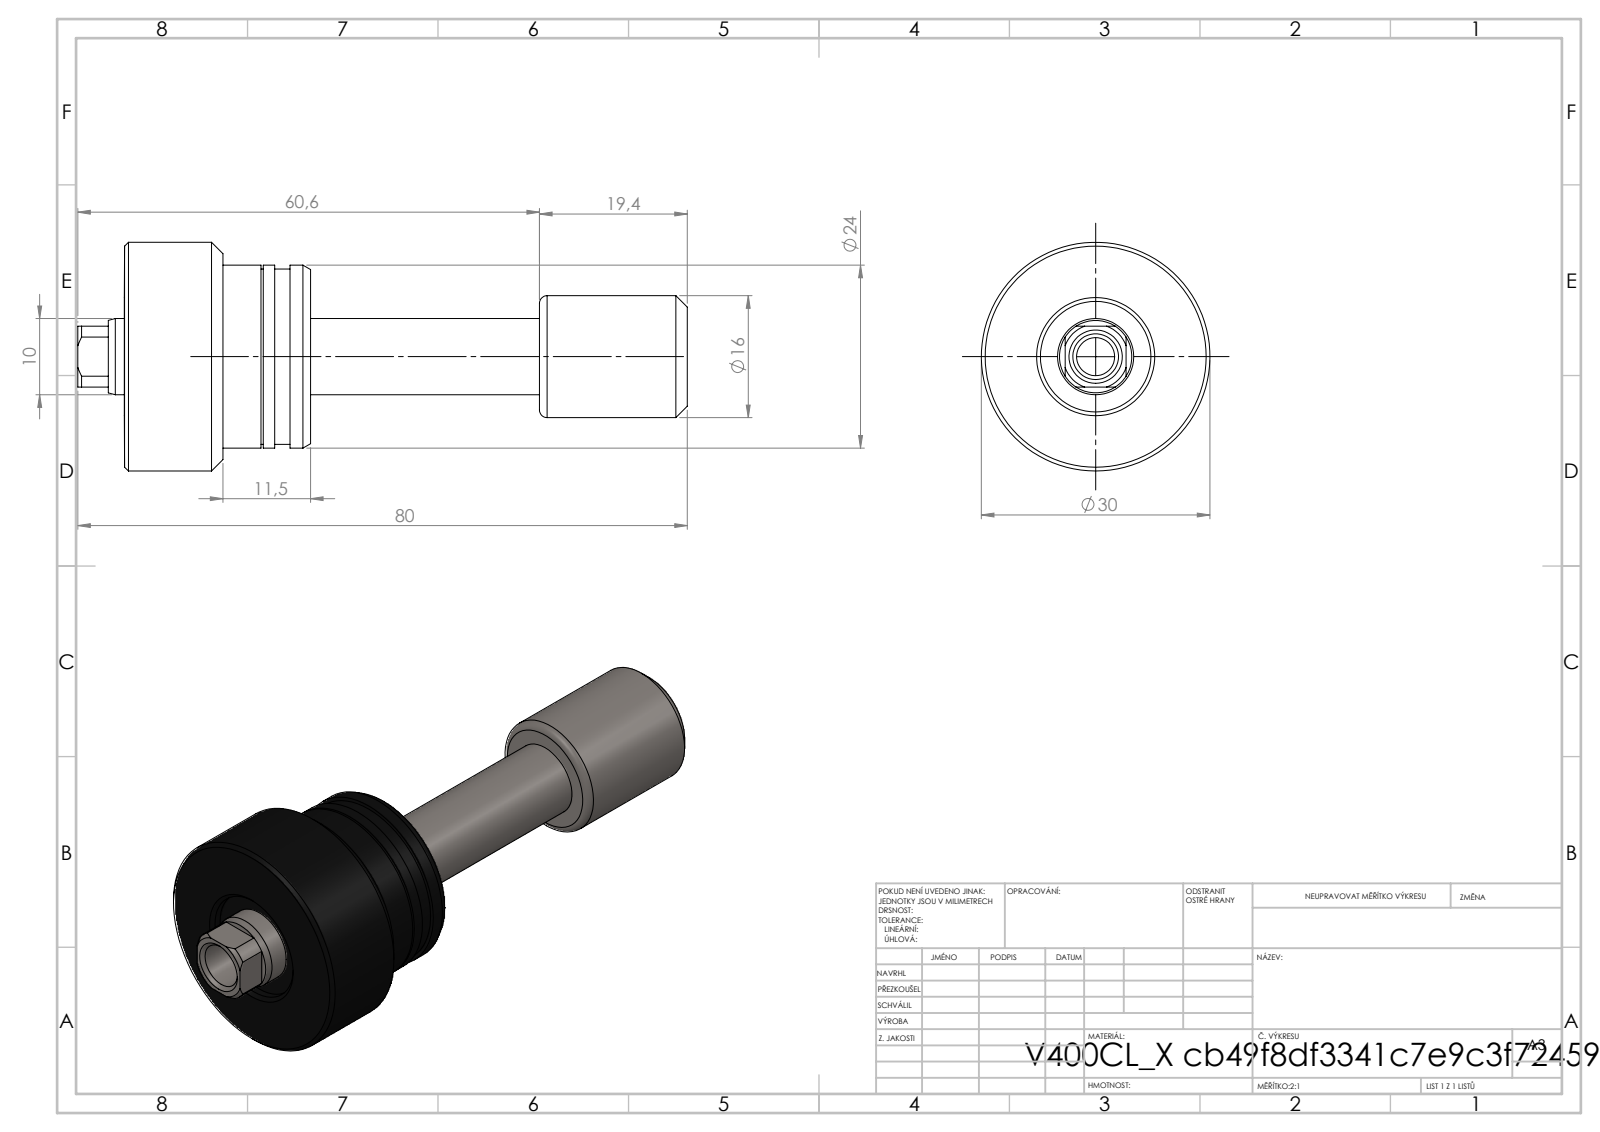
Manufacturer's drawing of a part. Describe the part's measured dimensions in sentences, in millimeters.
The part is named "V400CL_PC_X; V400CL_VC_X". Its 3-D file was written by "SolidWorks 2019 (CONFIG_CONTROL_DESIGN)". It is 2 solids with 79 faces: 19 planar, 30 cylindrical and 30 other. Overall it measures 80 by 30 by 30 millimeters. Its volume is 19 995 cubic millimeters and its surface area 7 685 square millimeters. Round holes: 1 of diameter 2.05, 1 of diameter 5, 1 of diameter 6, 1 of diameter 10, 1 of diameter 14.5. Round bosses or shafts: 1 of diameter 30, 1 of diameter 24, 1 of diameter 23, 1 of diameter 16. Partial cylindrical surfaces (rounded edges, fillets, slot ends): 1 of radius 4.75. The main face-to-face distances are 11.5, 49.45, 60.95, 72.45, 23, 19.4, 30.05, 41.55, 53.05, 8.
